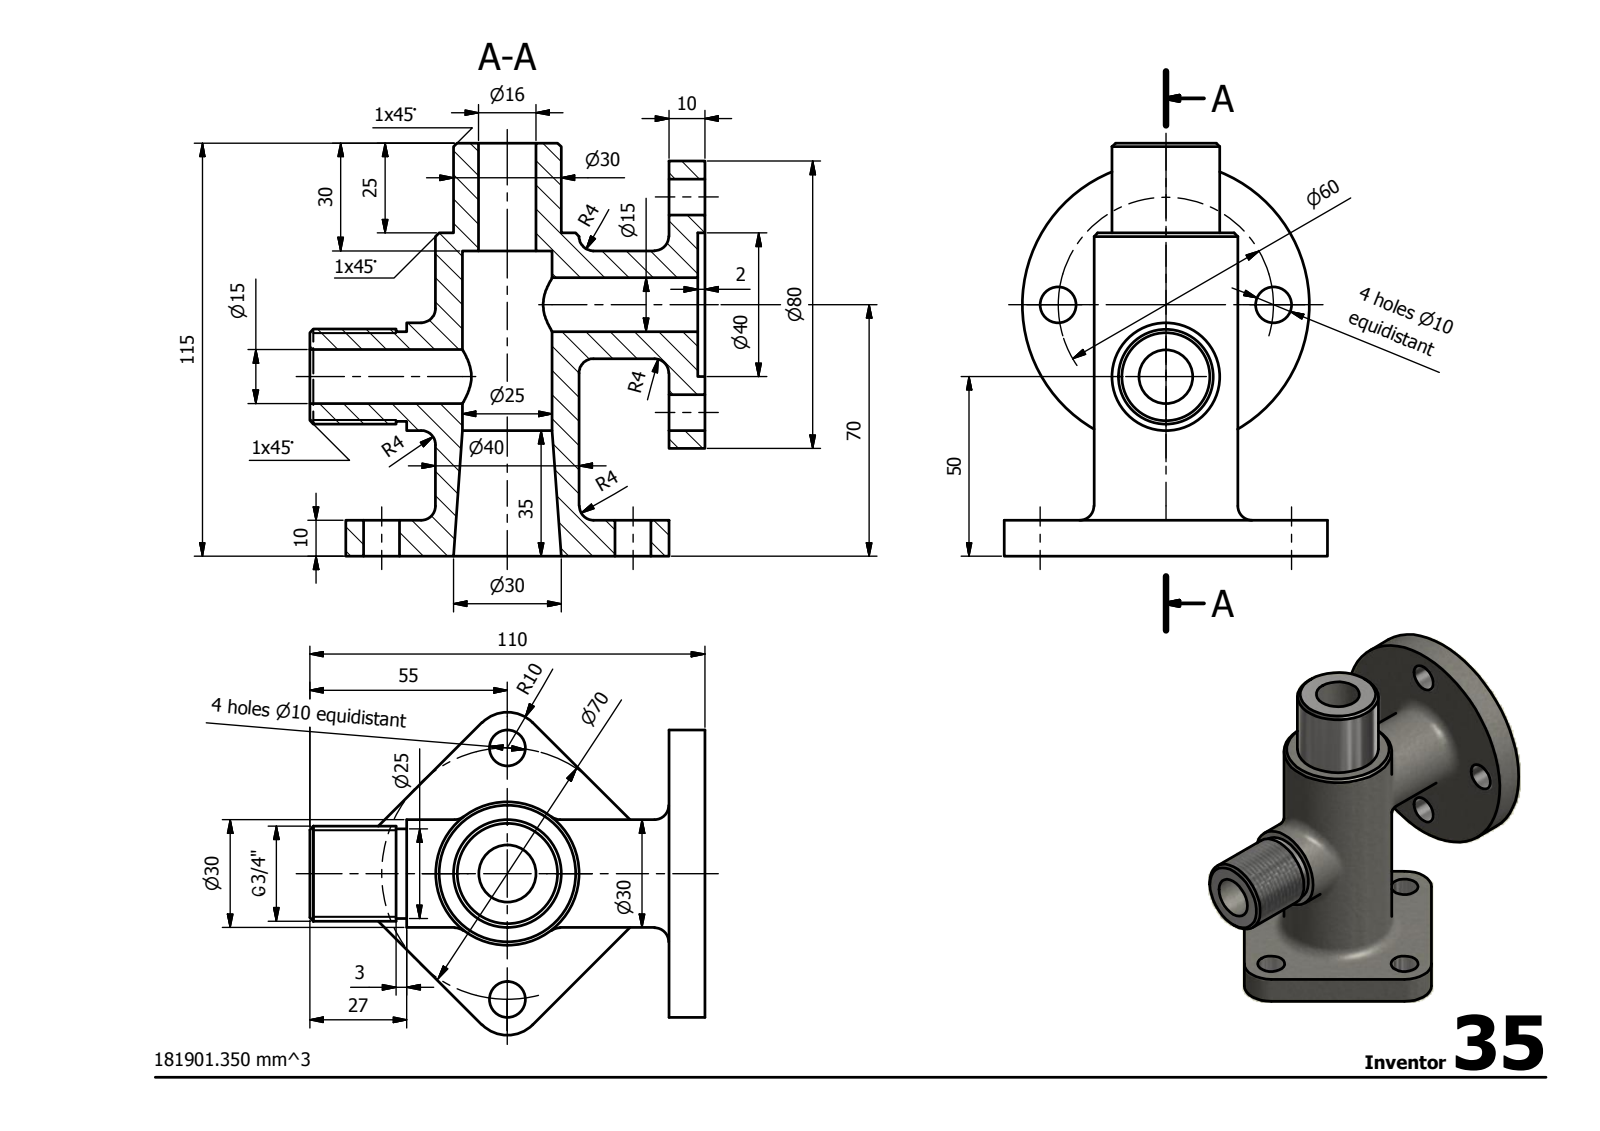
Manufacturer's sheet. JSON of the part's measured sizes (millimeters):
{"step_written_by": "Autodesk Inventor 2014 (AUTOMOTIVE_DESIGN)", "units": "millimeters", "bodies": {"solids": 1, "faces": 47, "planar": 15, "cylindrical": 24, "other": 8}, "overall_size": [115, 110, 90], "volume_mm3": 74847, "surface_area_mm2": 36811, "round_holes": [[10, 8], [15, 2], [16, 1], [25, 1], [40, 1]], "round_bosses_or_shafts": [[30, 3], [80, 1], [40, 1], [26.44, 1], [25, 1]], "partial_cylinders_radius": [[10, 4]], "face_to_face_distances": [10, 8, 2, 69.48, 90, 80, 115, 105, 25, 100], "hole_center_spacings": [30, 35, 42.43, 49.5, 36.06, 60, 70, 10]}
